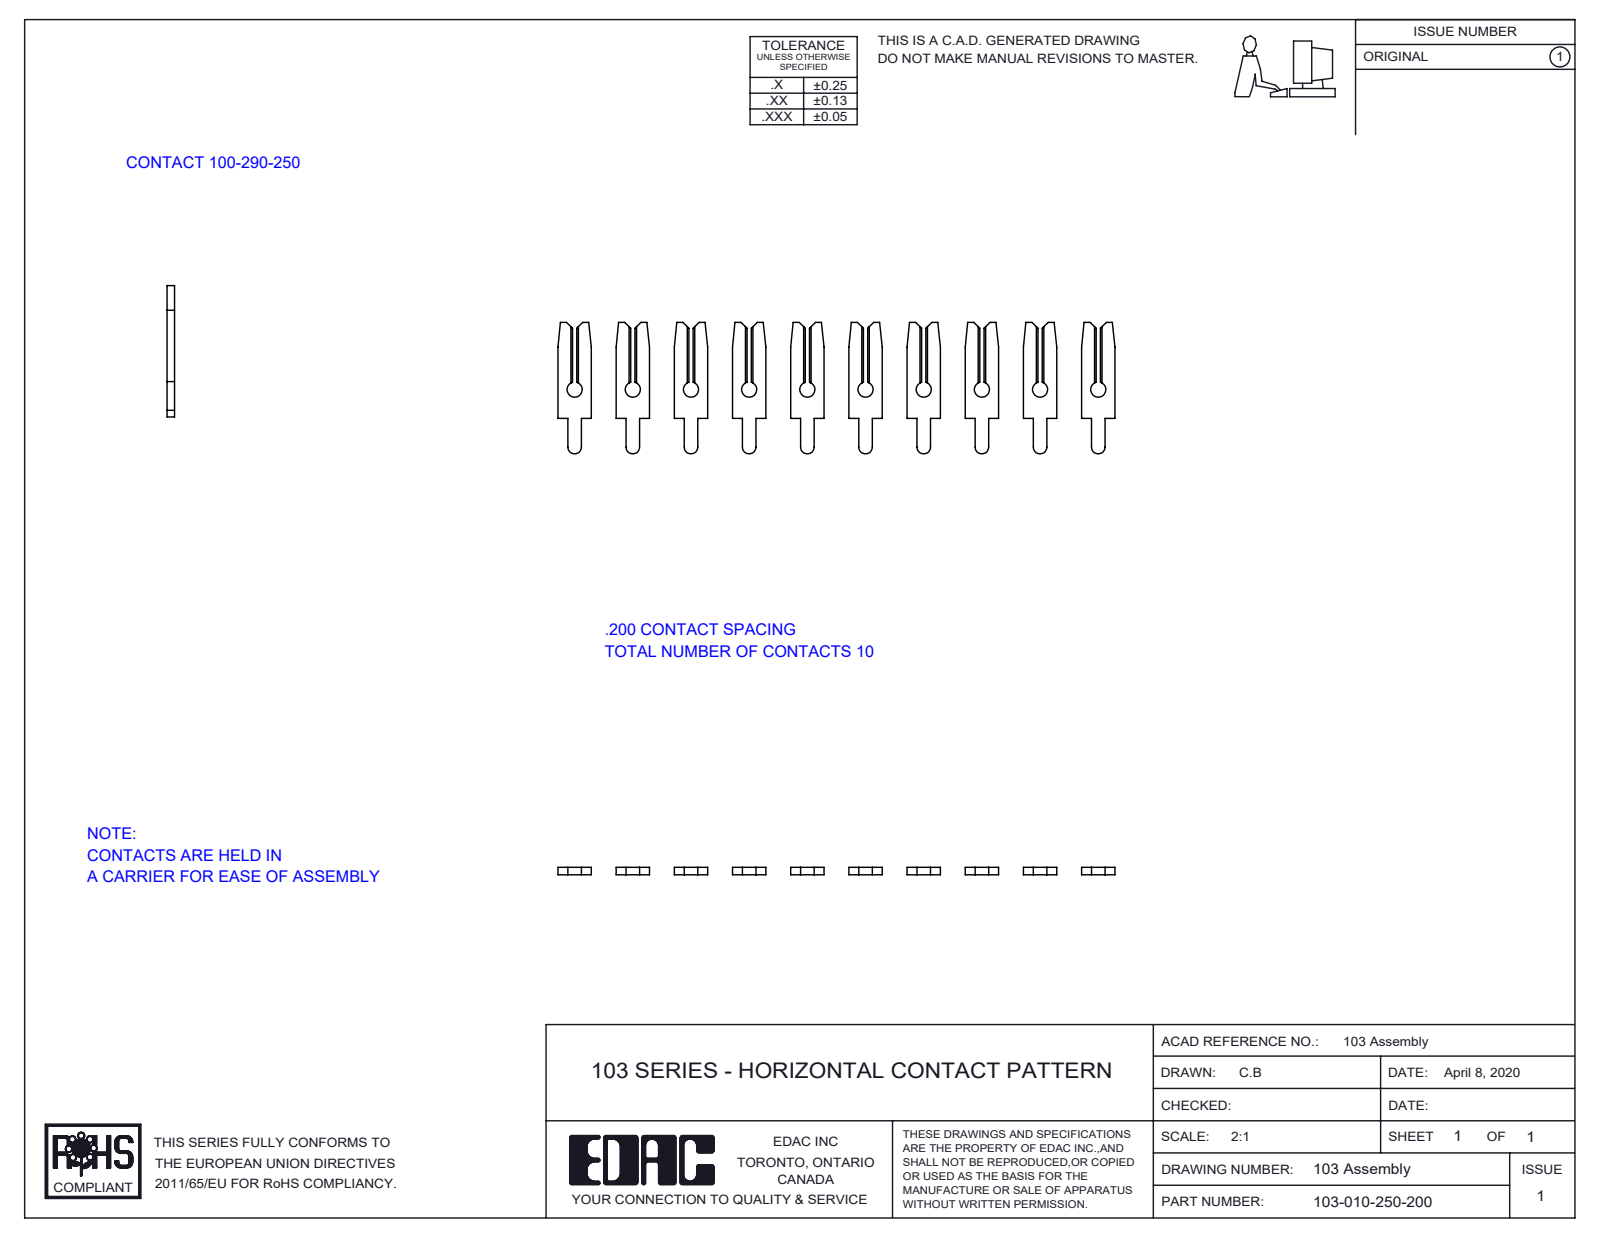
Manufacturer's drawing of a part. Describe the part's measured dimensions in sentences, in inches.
The part is named "100-290-001_100-290-250; 103-010-250-200". Its 3-D file was written by "SolidWorks 2016 (CONFIG_CONTROL_DESIGN)". It is 10 solids with 240 faces: 200 planar, 40 cylindrical and 0 other. Overall it measures 1.915 by 0.452 by 0.026 inches. Its volume is 0.01 cubic inches and its surface area 1.137 square inches. Round holes: 10 of diameter 0.052. Partial cylindrical surfaces (rounded edges, fillets, slot ends): 10 of radius 0.024. The main face-to-face distances are 0.026, 0.2, 0.4, 0.6, 0.8, 0.115, 1, 0.315, 0.085, 0.141. The hole center spacings are 0.2, 0.4, 0.6, 0.8, 1, 1.2, 1.4, 1.6.
